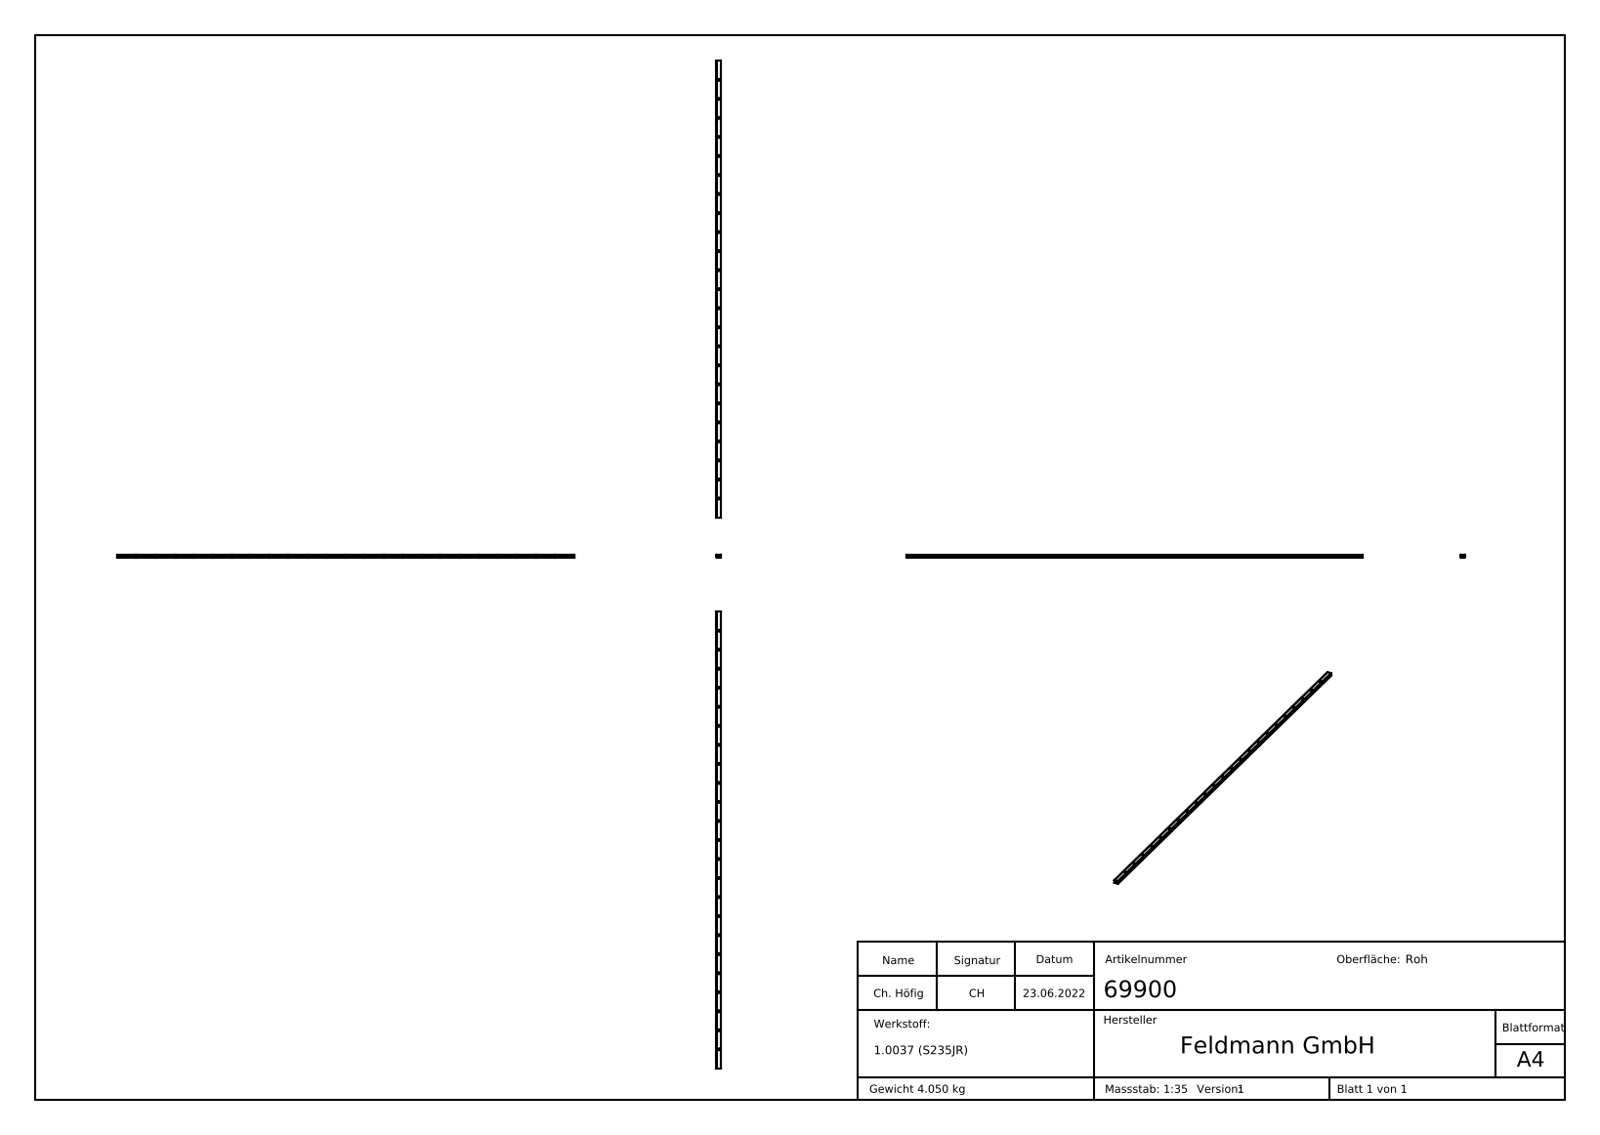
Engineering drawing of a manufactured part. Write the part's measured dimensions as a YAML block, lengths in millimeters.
part_name: "69900"
step_written_by: "SolidWorks 2018 (CONFIG_CONTROL_DESIGN)"
units: millimeters
bodies: {solids: 1, faces: 284, planar: 117, cylindrical: 54, other: 113}
overall_size: [3000, 30, 20]
volume: 519186
surface_area: 523309
round_holes:
  - {diameter: 13, count: 23}
partial_cylinders:
  - {radius: 1, count: 4}
  - {radius: 3, count: 4}
face_to_face_distances: [2, 18, 28, 16, 20, 30, 26, 3000, 1.9, 26.1]
hole_center_spacings: [125, 250, 375, 500, 625, 750, 875, 1000]
